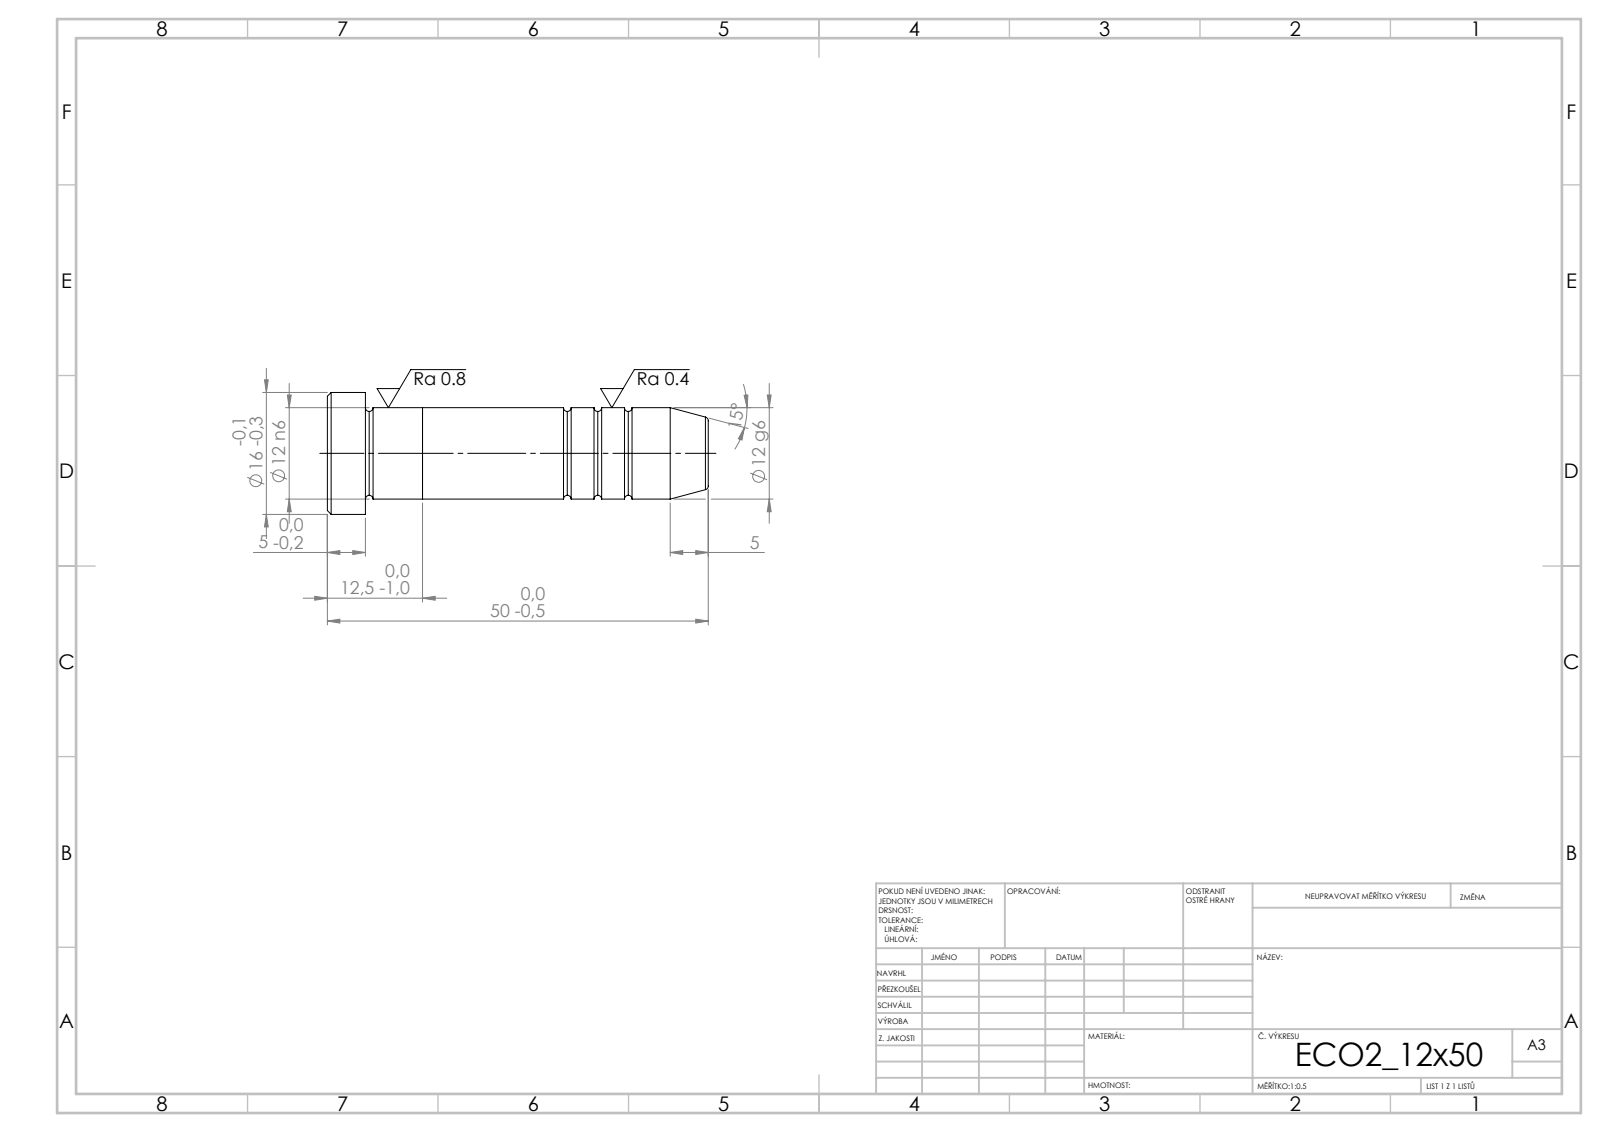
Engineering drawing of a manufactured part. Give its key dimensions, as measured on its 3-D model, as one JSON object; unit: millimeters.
{"step_written_by": "SolidWorks 2019 (CONFIG_CONTROL_DESIGN)", "units": "millimeters", "bodies": {"solids": 2, "faces": 39, "planar": 5, "cylindrical": 12, "other": 22}, "overall_size": [50, 16, 16], "volume_mm3": 5914, "surface_area_mm2": 2571, "round_bosses_or_shafts": [[16, 1], [12, 1]], "face_to_face_distances": [12.5, 7.5, 5, 37.5, 45, 50]}
